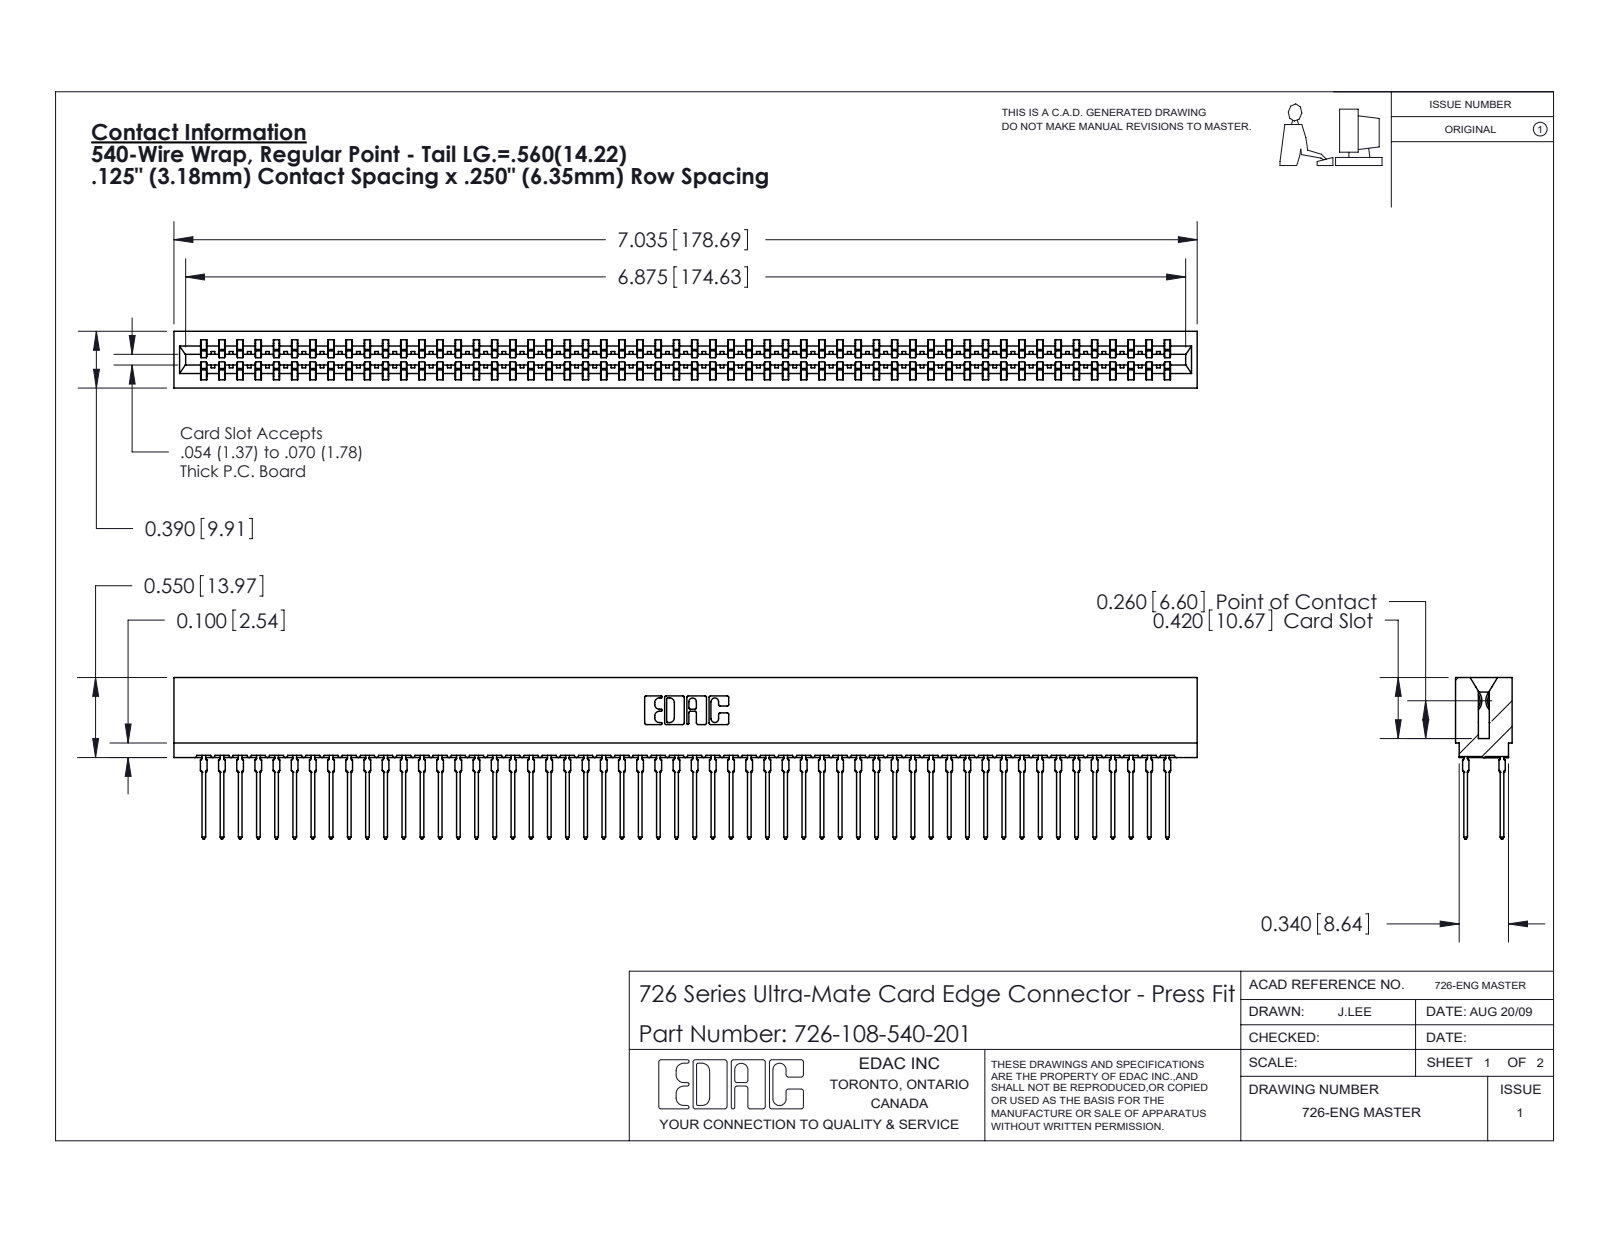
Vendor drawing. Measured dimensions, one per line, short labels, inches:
name: 726-108-540-201; 726 Part_.515 Slot Depth - 01; 746-292-001_540
written by: SolidWorks 2020 (CONFIG_CONTROL_DESIGN)
unit: in
bodies: 108 solids, 9763 faces (5023 planar, 1932 cylindrical, 2808 other)
size: 7.035 × 1.109 × 0.39
volume: 0.085 in³; area: 45.83 in²
rounds: 216× R0.021, 55× R0.015, 22× R0.01, 8× R0.005, 8× R0.011, 6× R0.007, 6× R0.031, 3× R0.026
face distances: 0.057, 0.333, 0.025, 0.307, 0.39, 0.25, 0.275, 0.083, 0.365, 0.032
